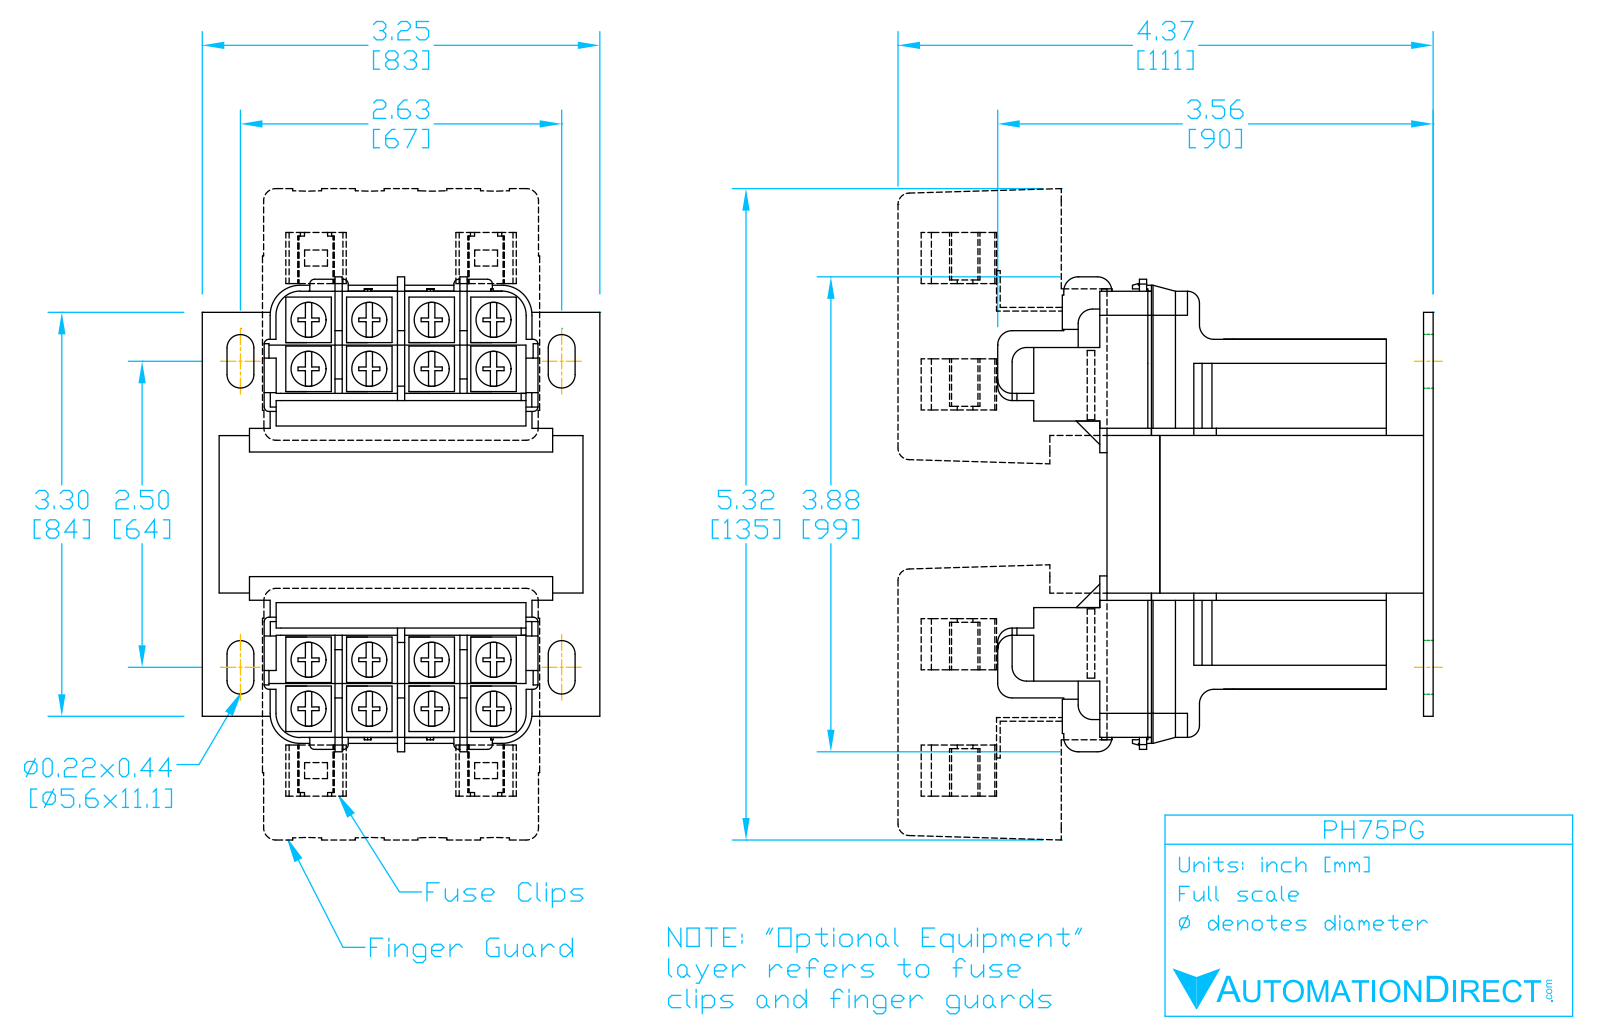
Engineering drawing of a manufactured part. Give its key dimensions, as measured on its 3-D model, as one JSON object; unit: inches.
{"part_name": "PH75PG", "step_written_by": "SolidWorks 2017 (AUTOMOTIVE_DESIGN)", "units": "inches", "bodies": {"solids": 8, "faces": 500, "planar": 296, "cylindrical": 140, "other": 64}, "overall_size": [3.78, 3.474, 3.25], "volume_in3": 23.32, "surface_area_in2": 111.2, "round_holes": [[0.157, 4]], "partial_cylinders_radius": [[0.039, 40], [0.079, 28], [0.11, 8], [0.197, 8], [0.118, 4], [0.246, 4]], "face_to_face_distances": [1.181, 2.136, 0.364, 2, 0.136, 0.398, 2.602, 2.362, 2.5, 1.26], "hole_center_spacings": [0.875, 2.624, 2.767]}
